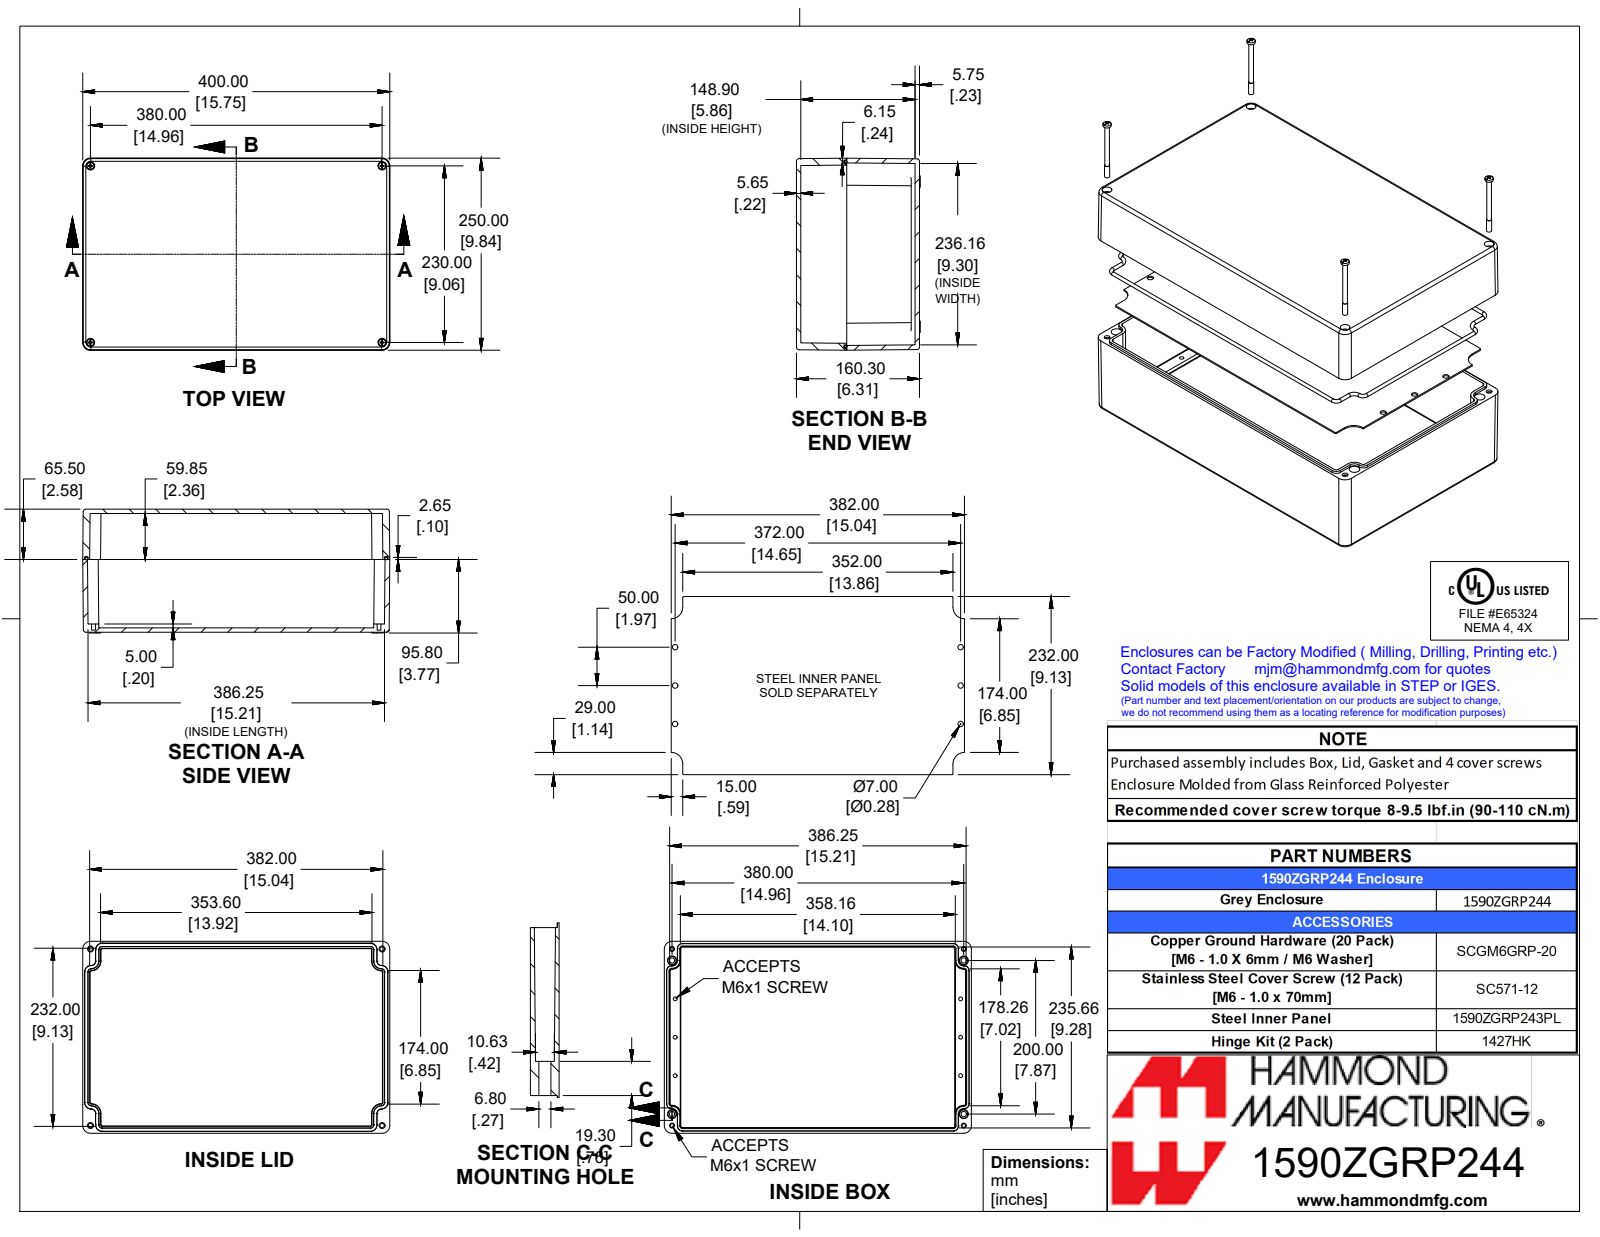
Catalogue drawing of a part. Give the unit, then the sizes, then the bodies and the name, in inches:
Units: inches
Overall size (bounding box): 15.748 × 9.843 × 6.339
Round holes (diameter × count): ⌀0.194 ×10, ⌀0.276 ×6, ⌀0.236 ×4, ⌀0.252 ×4, ⌀0.268 ×4, ⌀0.425 ×4
Round bosses / shafts (diameter × count): ⌀0.169 ×6, ⌀0.229 ×4, ⌀0.206 ×4
Partial cylindrical surfaces — rounded edges, fillets, slot ends (radius × count): R0.394 ×8, R0.02 ×6, R0.118 ×4, R0.138 ×4, R0.591 ×4
Main face-to-face distances: 5.874, 0.197, 6.299, 0.25, 0.425, 0.498, 0.073, 5.801, 6.102, 5.677
Hole centre spacings: 0.575, 1.969, 1.975, 2.548, 3.94, 4.515, 5.907, 6.482
Volume: 174.5 in³ · Surface area: 1 566 in²
Bodies: 8 solids, 455 faces (253 planar, 74 cylindrical, 128 other)
Part name (STEP PRODUCT): 1590ZGRP244
STEP written by: SolidWorks 2019 (CONFIG_CONTROL_DESIGN)
